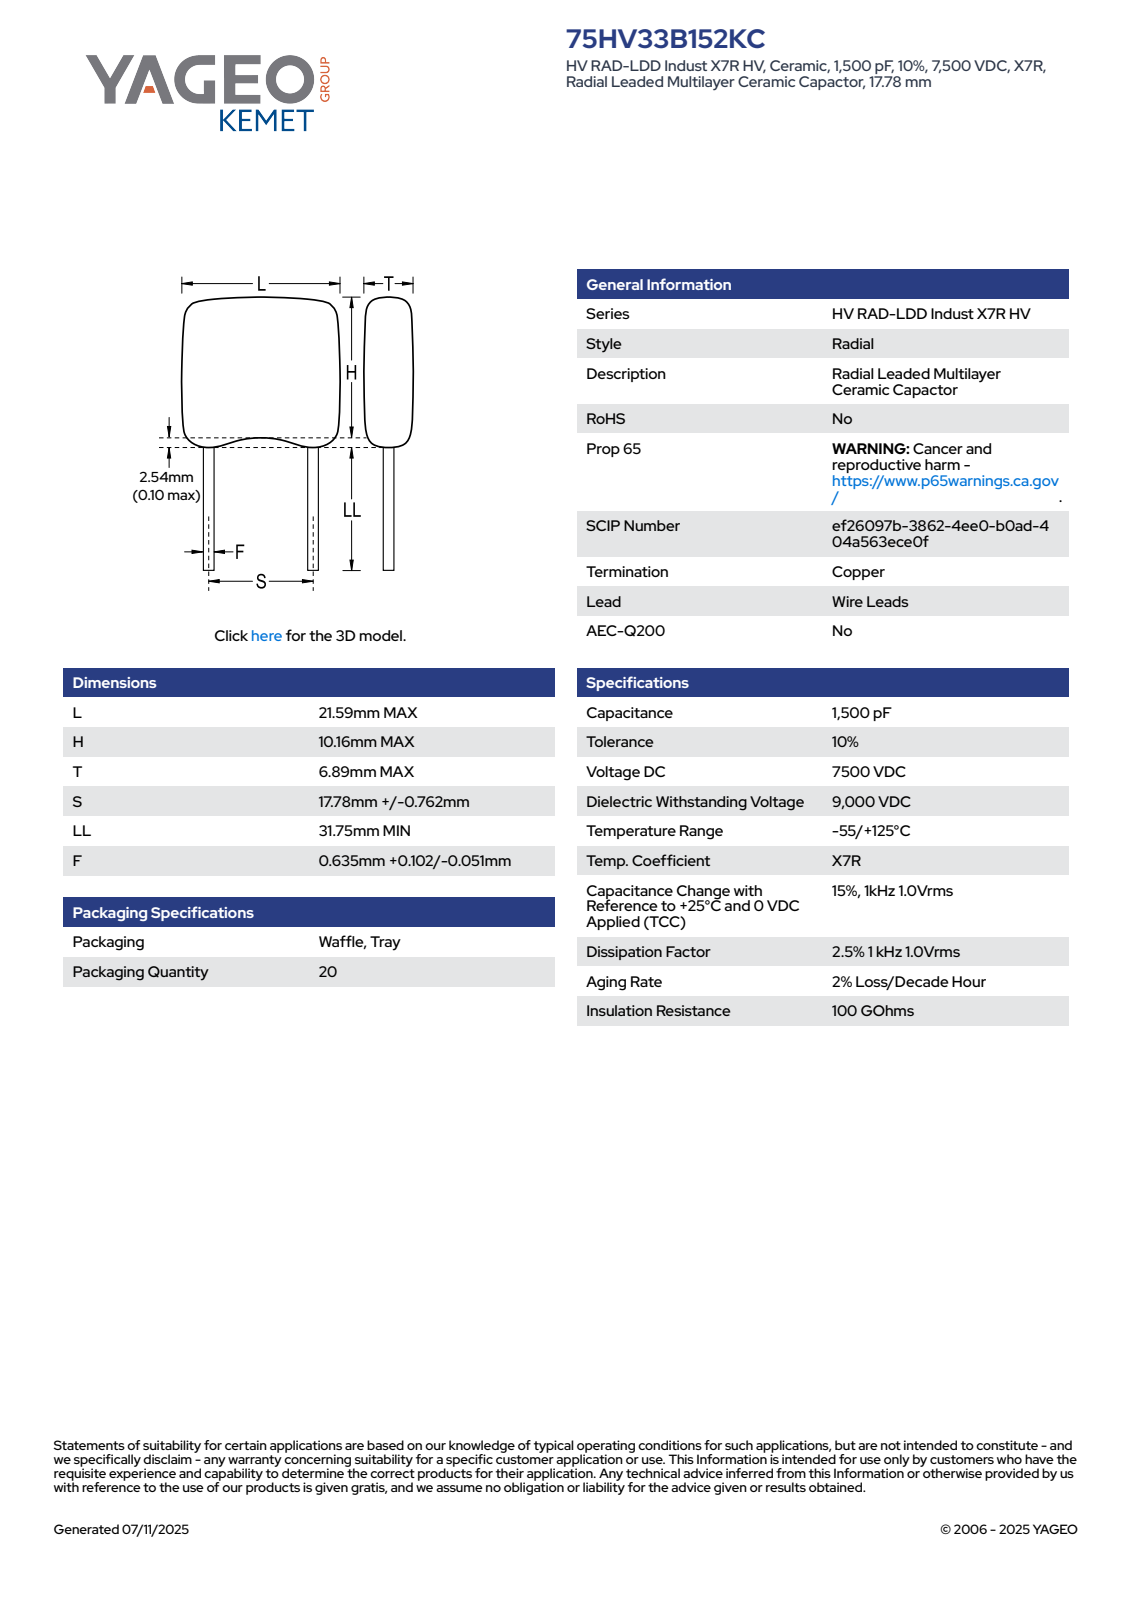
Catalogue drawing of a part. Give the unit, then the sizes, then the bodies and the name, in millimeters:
Units: millimetres
Overall size (bounding box): 43.43 × 21.59 × 5.08
Round bosses / shafts (diameter × count): ⌀0.64 ×2
Partial cylindrical surfaces — rounded edges, fillets, slot ends (radius × count): R0.5 ×8, R2 ×4
Main face-to-face distances: 5.08, 21.59, 11.68, 31.75, 43.43, 40.19, 8.44, 3.24, 36.76, 5.01
Volume: 1 156 mm³ · Surface area: 932 mm²
Bodies: 4 solids, 92 faces (66 planar, 16 cylindrical, 10 other)
Part name (STEP PRODUCT): CCRM_RCST_HV33_L21.59H10.16T6.89S17.78LL3.175F0.737
STEP written by: SolidWorks 2021 (AUTOMOTIVE_DESIGN)
